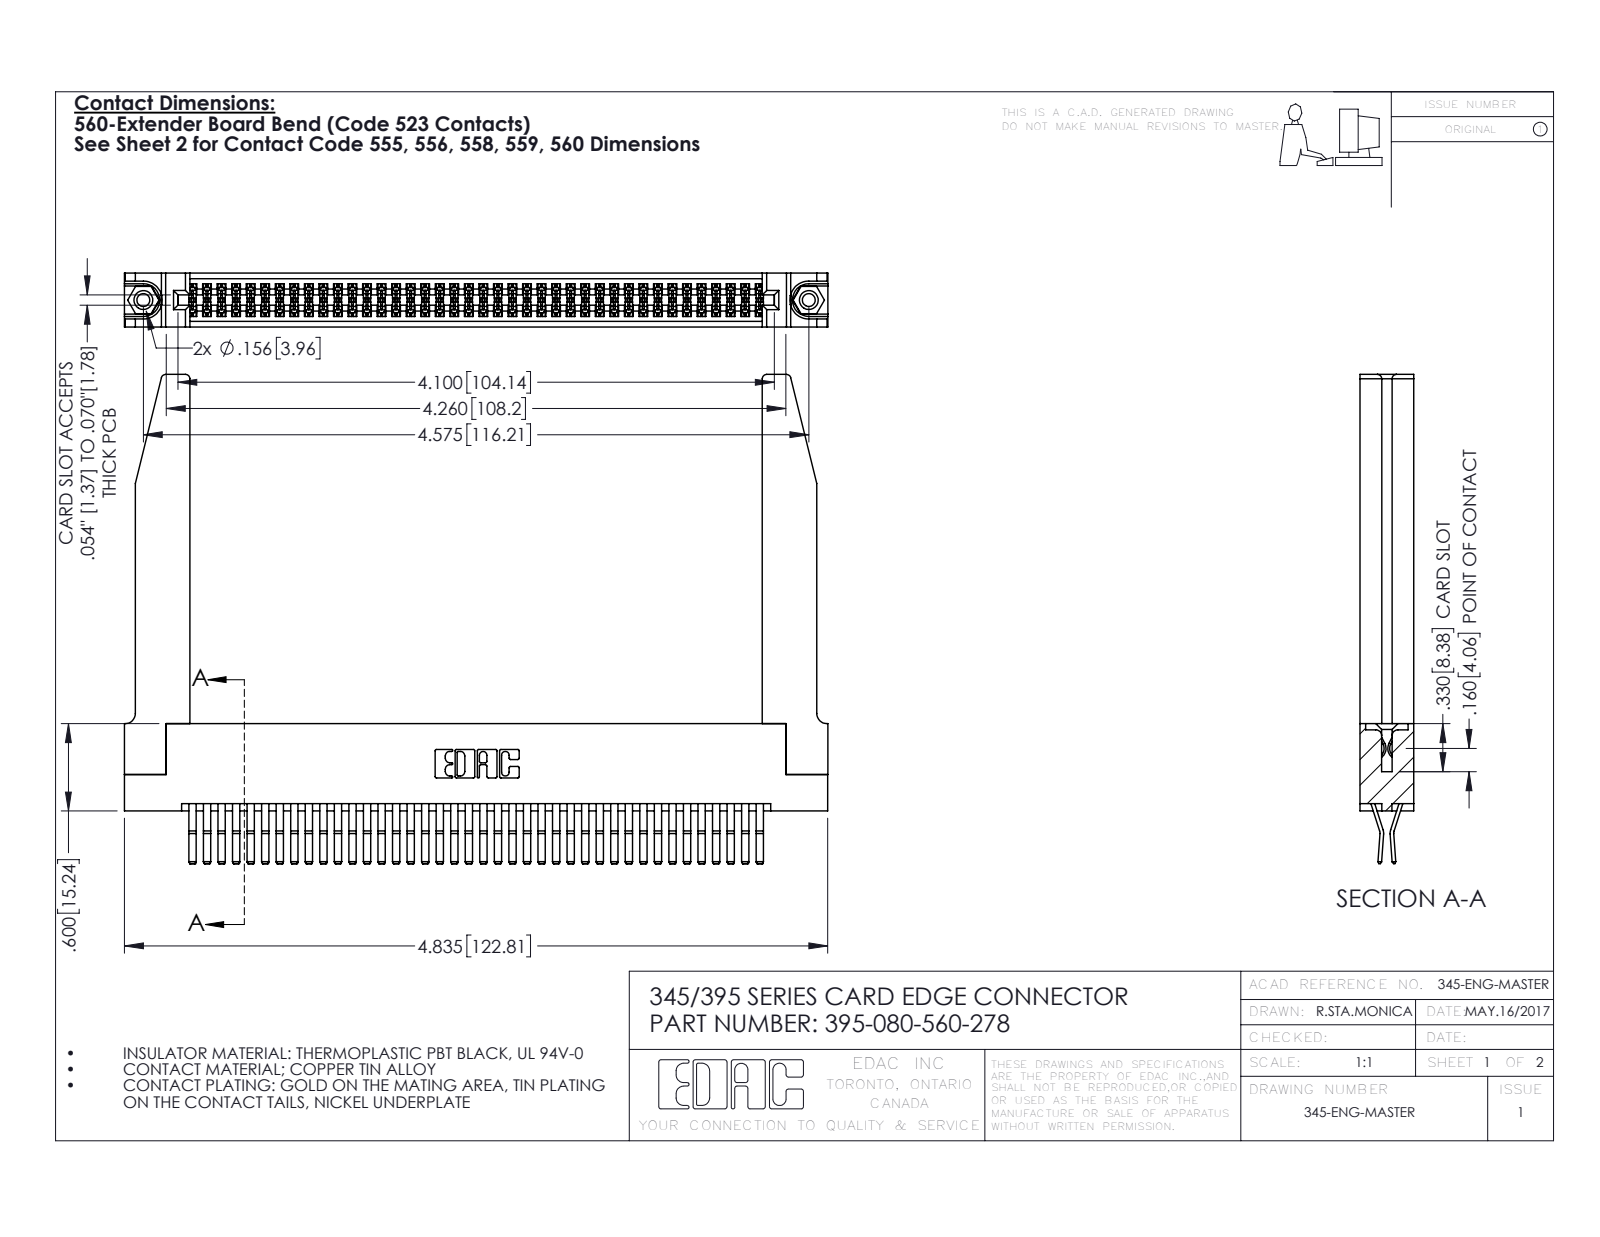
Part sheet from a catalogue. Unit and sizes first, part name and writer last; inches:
Units: inches
Overall size (bounding box): 4.836 × 3.362 × 0.37
Round holes (diameter × count): ⌀0.089 ×2, ⌀0.125 ×2, ⌀0.156 ×2, ⌀0.064 ×1
Round bosses / shafts (diameter × count): ⌀0.155 ×2
Partial cylindrical surfaces — rounded edges, fillets, slot ends (radius × count): R0.006 ×120, R0.01 ×22, R0.03 ×8, R0.007 ×6, R0.031 ×6, R0.026 ×3, R0.01 ×2, R0.014 ×2
Main face-to-face distances: 0.37, 0.072, 0.298, 0.025, 0.2, 0.098, 0.272, 0.225, 0.148, 0.15
Hole centre spacings: 0.27, 4.339, 4.575
Volume: 1.233 in³ · Surface area: 41.13 in²
Bodies: 85 solids, 4520 faces (2862 planar, 1606 cylindrical, 52 other)
Part name (STEP PRODUCT): 345 Part_Flush Mounting Lugs - 0.156 Dia-TH; 345-250-001_345-250-001-102; 395-080-560-278; 345-292-001_560 Tail (+1 more)
STEP written by: SolidWorks 2016 (CONFIG_CONTROL_DESIGN)
